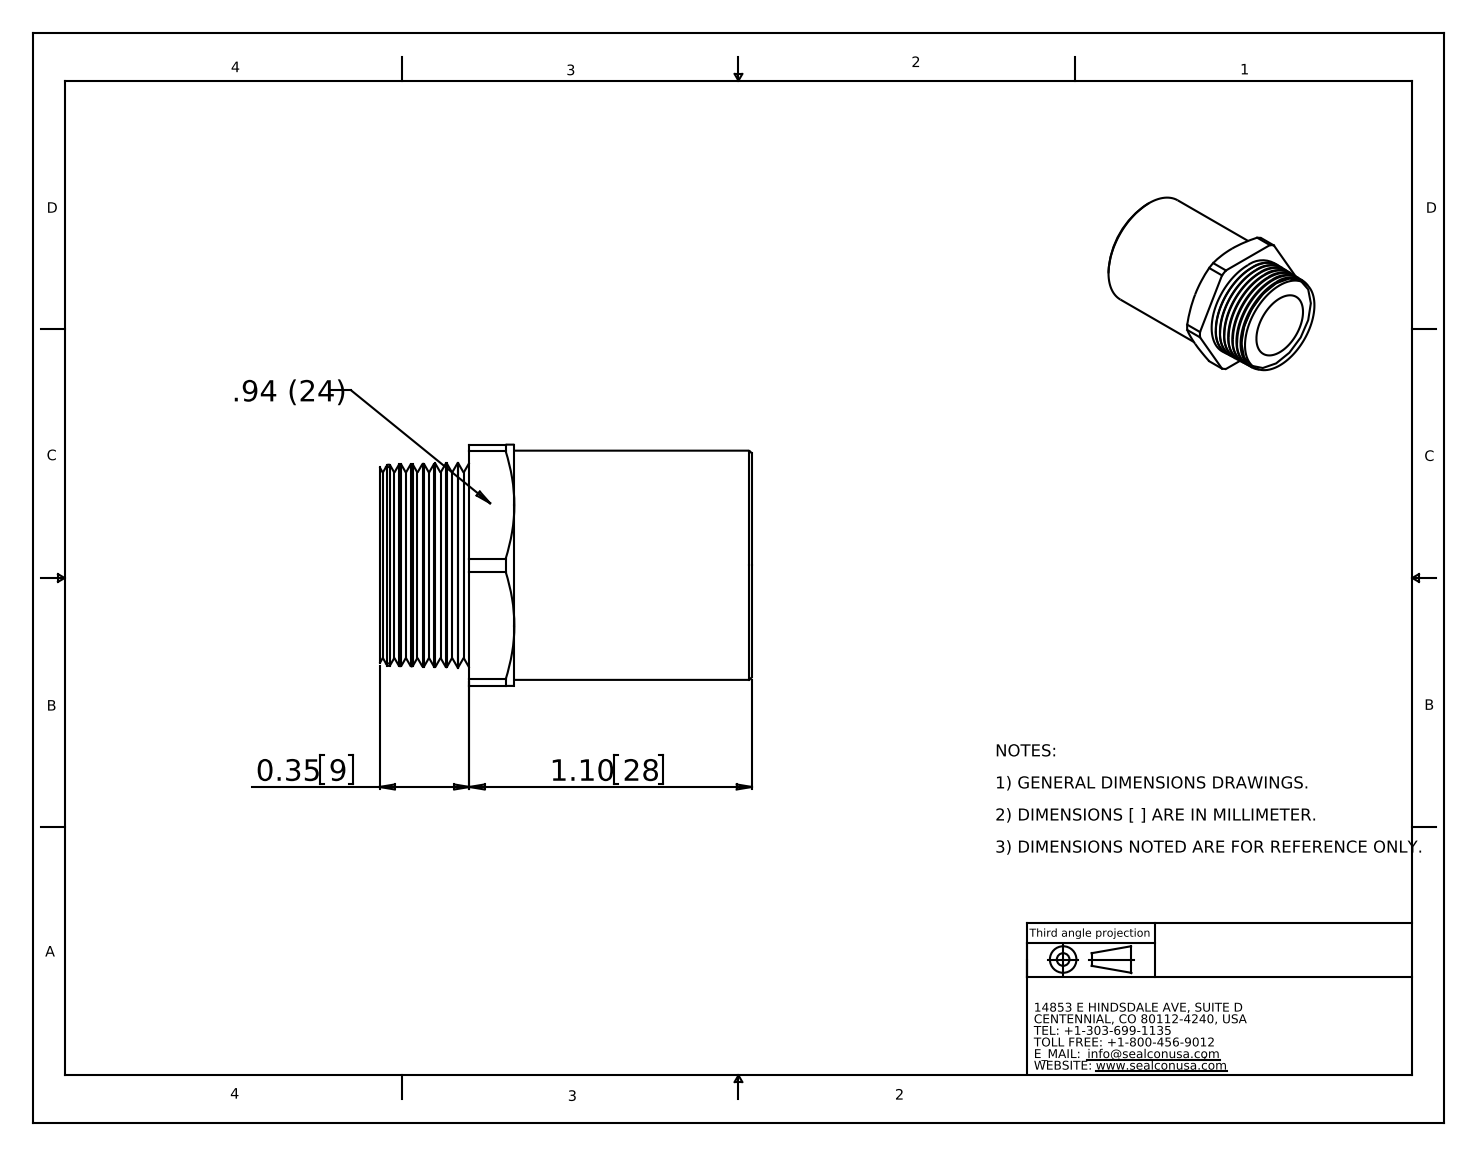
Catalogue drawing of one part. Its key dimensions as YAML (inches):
part_name: "SM13AA-BK"
step_written_by: "SolidWorks 2007 (AUTOMOTIVE_DESIGN)"
units: inches
bodies: {solids: 1, faces: 79, planar: 11, cylindrical: 11, other: 57}
overall_size: [1.45, 1.058, 0.94]
volume: 0.312
surface_area: 8.922
round_holes:
  - {diameter: 0.8, count: 1}
round_bosses_or_shafts:
  - {diameter: 0.893, count: 1}
partial_cylinders:
  - {radius: 0.529, count: 1}
face_to_face_distances: [0.175, 0.525, 0.35, 0.94, 0.925, 1.1, 1.45]
